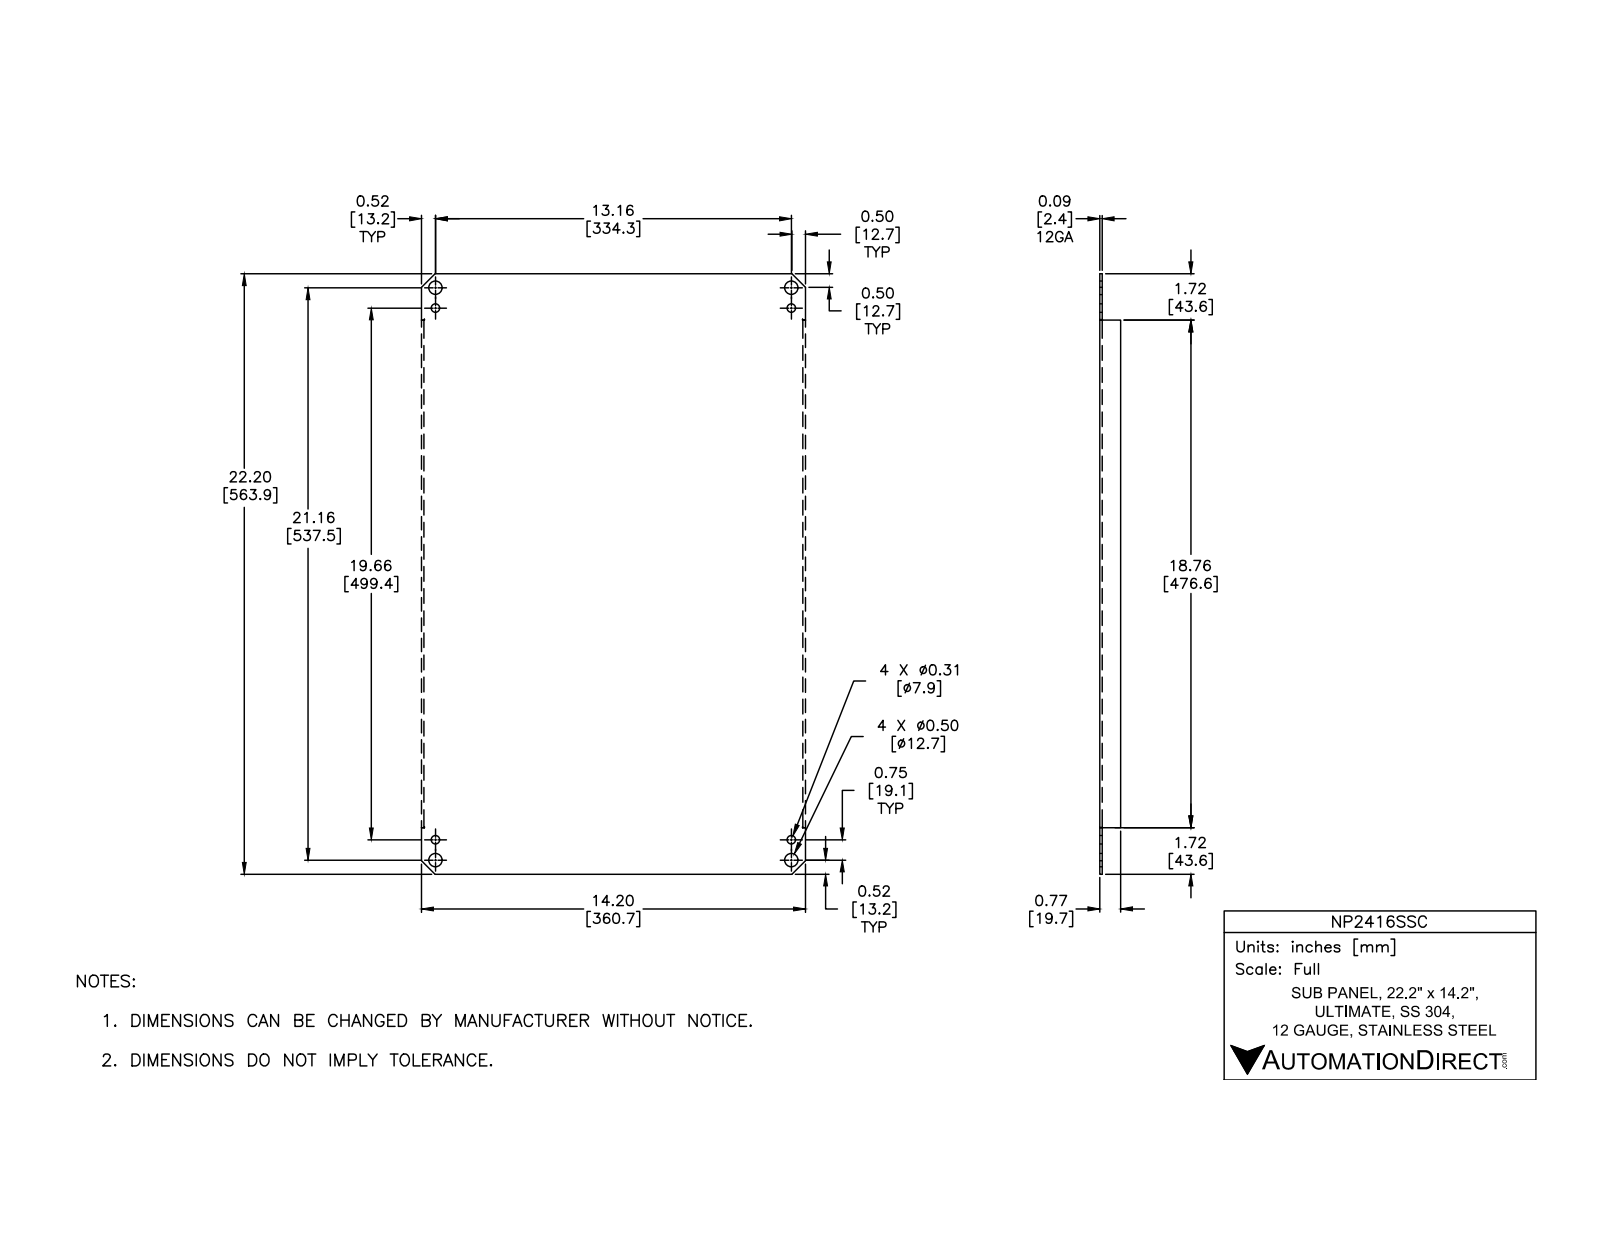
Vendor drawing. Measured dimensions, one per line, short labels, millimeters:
name: NP2416SSC
written by: Autodesk Inventor 2012 (AUTOMOTIVE_DESIGN)
unit: mm
bodies: 1 solid, 42 faces (30 planar, 12 cylindrical, 0 other)
size: 563.9 × 360.7 × 19.7
volume: 517 700 mm³; area: 439 900 mm²
holes: 4× ⌀8, 4× ⌀12.7
rounds: 2× R2.4, 2× R4.8
face distances: 2.4, 358.3, 360.7, 355.9, 17.3, 19.7, 563.9, 43.6, 520.2, 476.6
hole spacings: 19.1, 334.3, 334.8, 518.4, 616.8, 499.4, 537.5, 600.9
